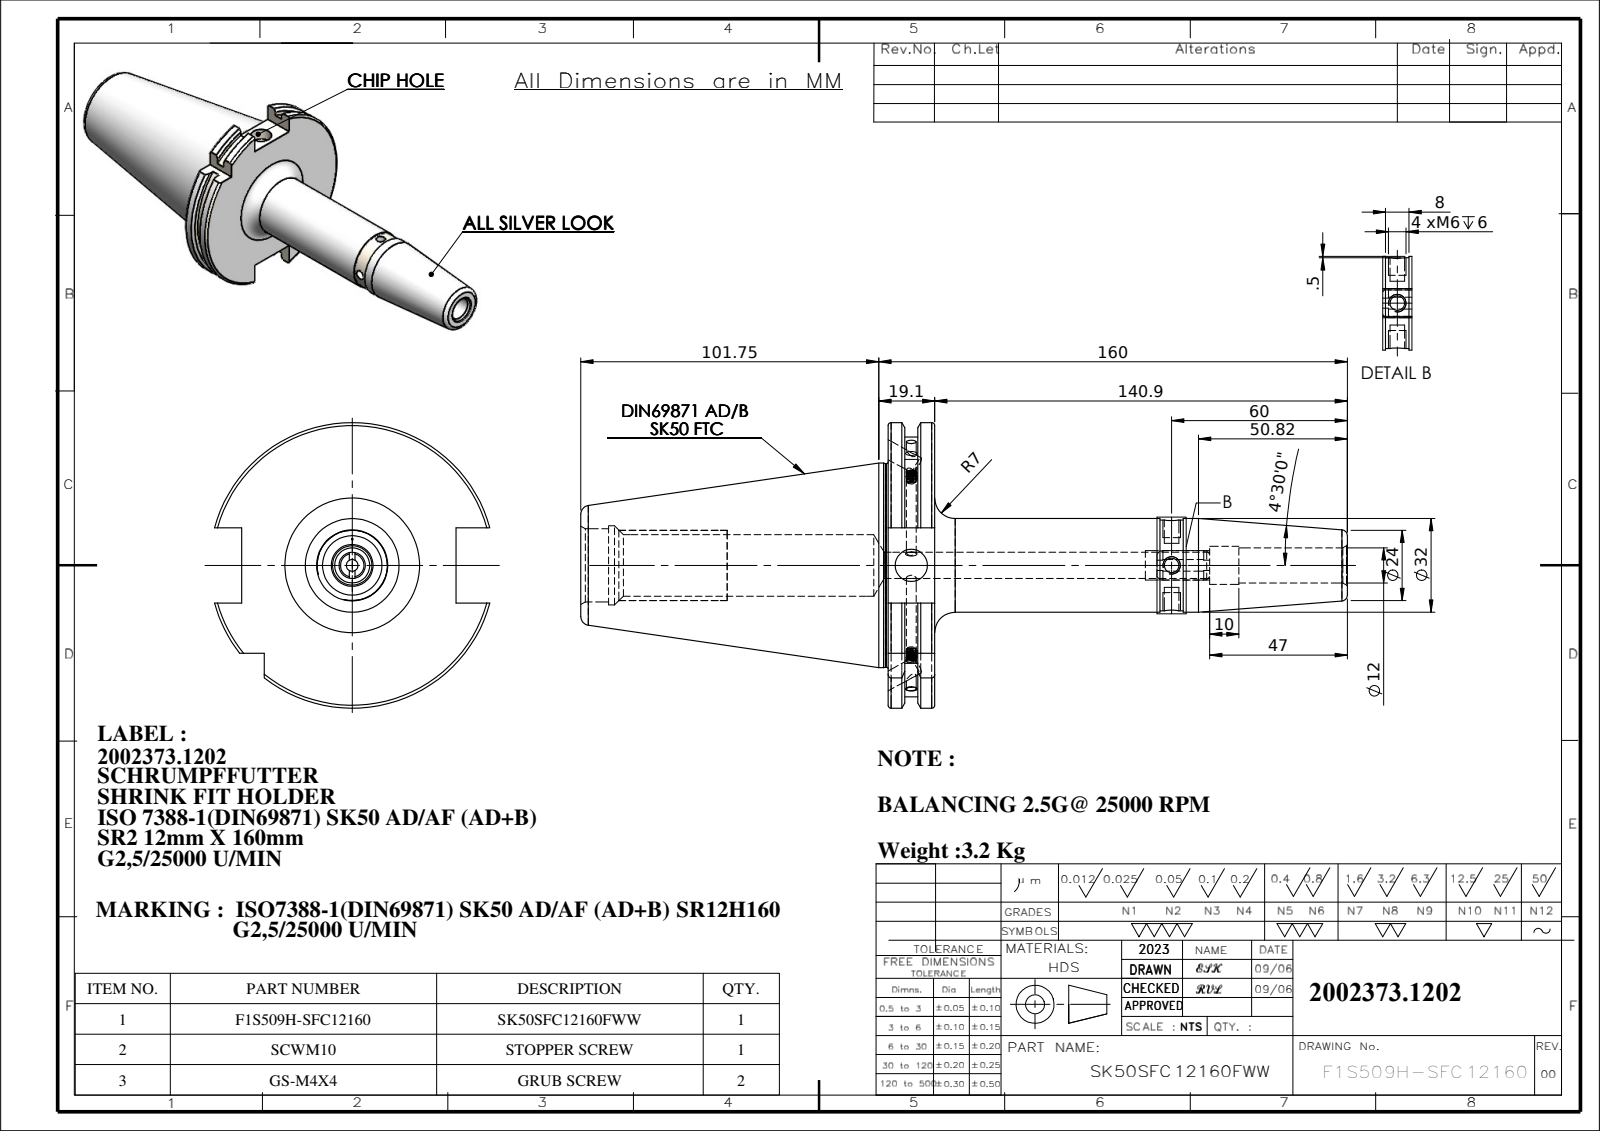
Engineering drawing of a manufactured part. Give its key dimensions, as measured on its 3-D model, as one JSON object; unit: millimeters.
{"part_name": "91506-SR212160; SK50SFC12160FWW; GS-M4X4_DIN 913 - M4 x 4-N; SCWM10", "step_written_by": "SolidWorks 2018 (CONFIG_CONTROL_DESIGN)", "units": "millimeters", "bodies": {"solids": 4, "faces": 248, "planar": 65, "cylindrical": 81, "other": 102}, "overall_size": [261.75, 97.5, 94.05], "volume_mm3": 416698, "surface_area_mm2": 63704, "round_holes": [[5, 2], [6, 2], [3.3, 1], [4, 1], [9, 1], [11, 1], [12, 1], [13, 1], [21, 1], [25, 1], [27, 1]], "round_bosses_or_shafts": [[4, 2], [69.85, 1], [69.45, 1], [32, 1], [31, 1], [10, 1]], "partial_cylinders_radius": [[44.9, 1], [48.75, 1]], "face_to_face_distances": [15.9, 5.65, 10.25, 10.14, 4.49, 5.76, 104.95, 110.6, 115.09, 120.85], "hole_center_spacings": [88.9]}
